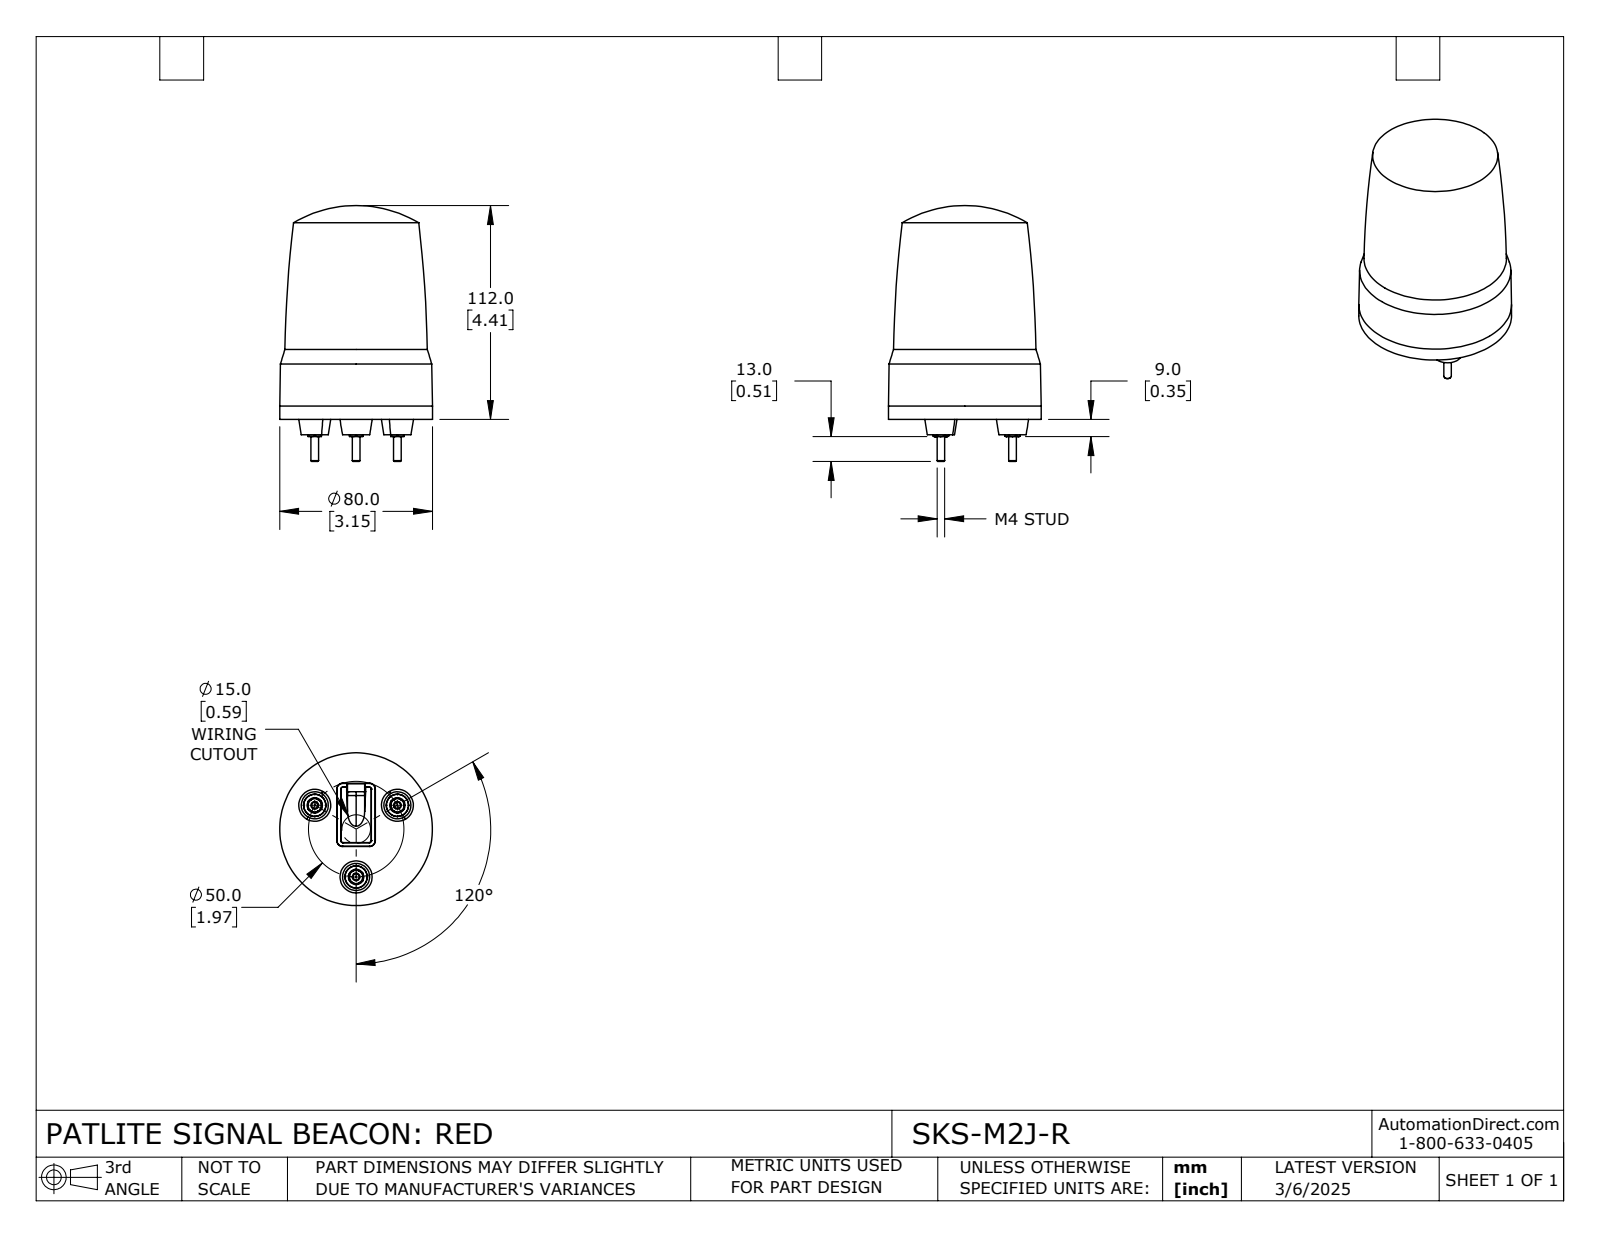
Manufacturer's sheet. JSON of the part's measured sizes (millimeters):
{"part_name": "SKS-M2J-R", "step_written_by": "SolidWorks 2024 (CONFIG_CONTROL_DESIGN)", "units": "millimeters", "bodies": {"solids": 1, "faces": 138, "planar": 47, "cylindrical": 14, "other": 77}, "overall_size": [134, 80, 80], "volume_mm3": 463225, "surface_area_mm2": 35408, "round_bosses_or_shafts": [[8, 3], [4, 3], [80, 1]], "face_to_face_distances": [0.85, 2.45, 1.6, 5.3, 6.15, 7.75, 2.7, 8, 8.85, 10.45]}
